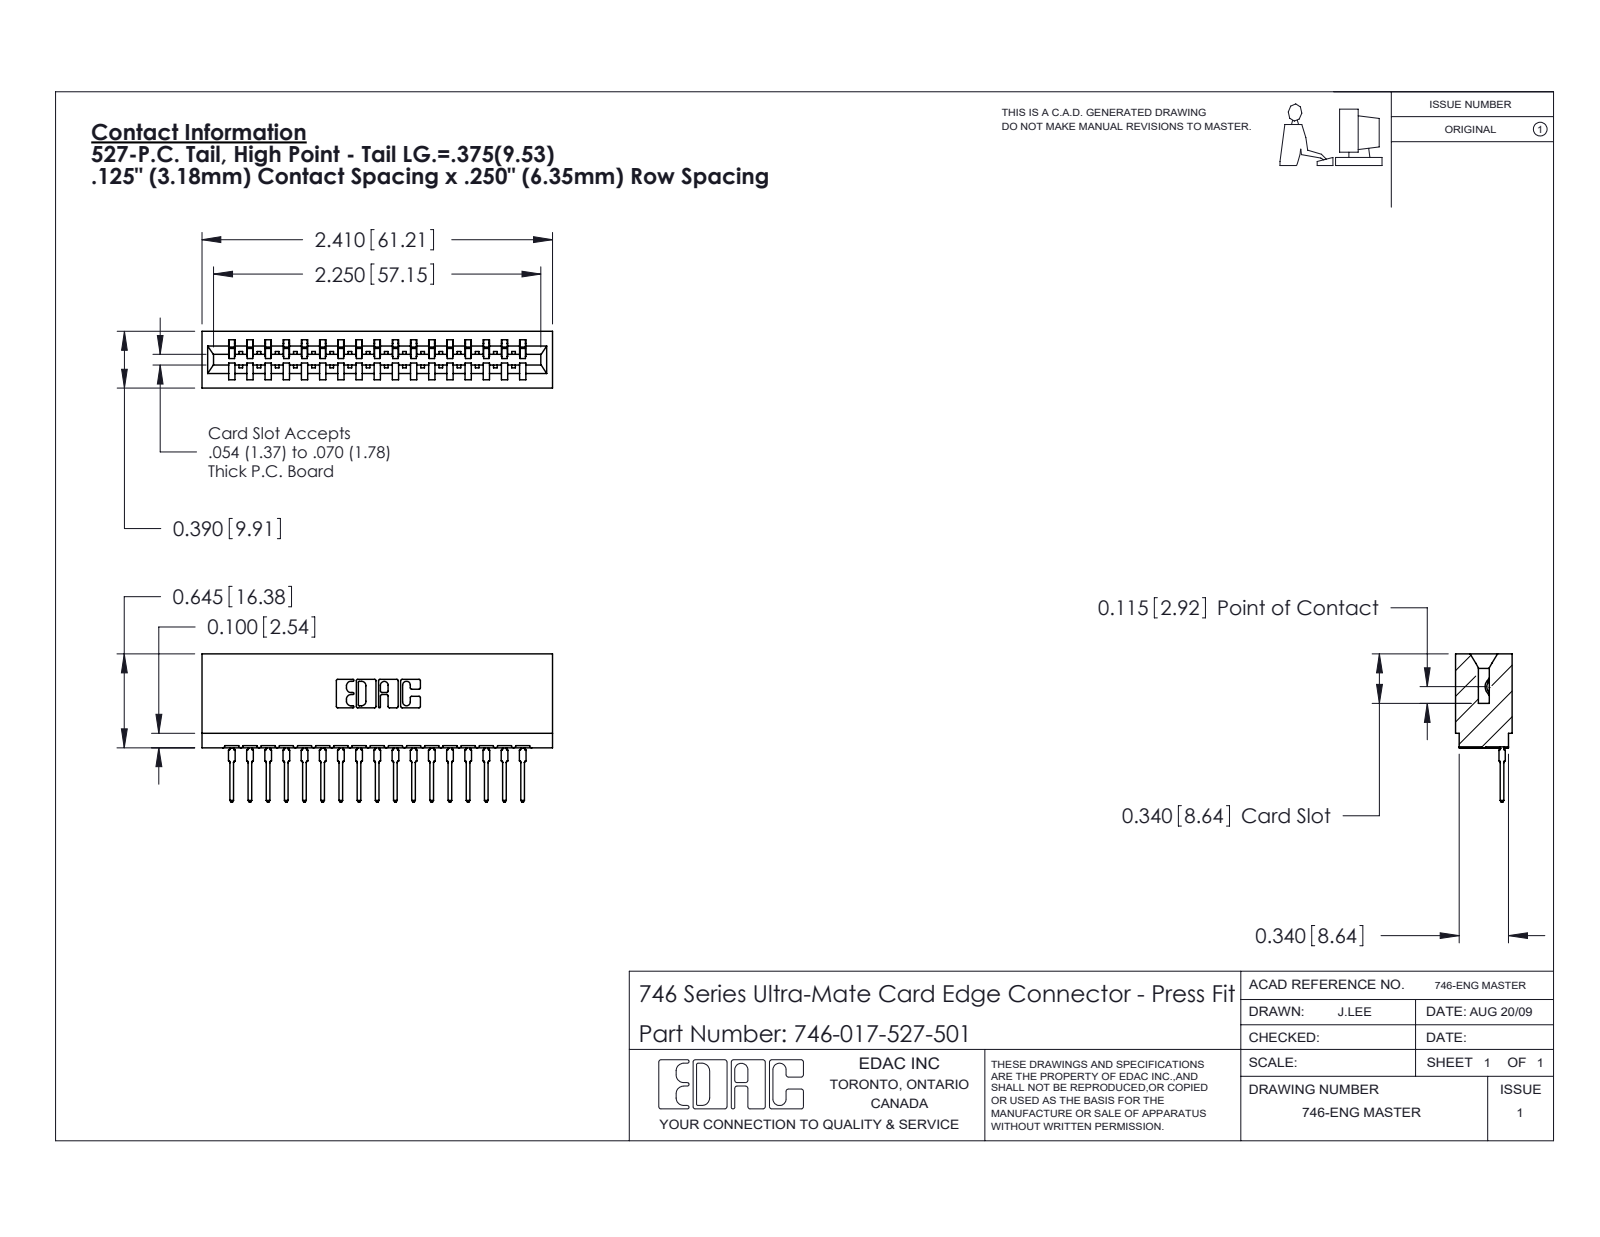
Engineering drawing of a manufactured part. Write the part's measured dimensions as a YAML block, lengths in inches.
part_name: "746-292-001_527; 746-017-527-501; 746 Part_.340 Slot Depth - 01"
step_written_by: "SolidWorks 2020 (CONFIG_CONTROL_DESIGN)"
units: inches
bodies: {solids: 18, faces: 1933, planar: 1126, cylindrical: 365, other: 442}
overall_size: [2.41, 1.019, 0.39]
volume: 0.43
surface_area: 14.28
partial_cylinders:
  - {radius: 0.021, count: 34}
  - {radius: 0.01, count: 22}
  - {radius: 0.015, count: 18}
  - {radius: 0.007, count: 6}
  - {radius: 0.031, count: 6}
  - {radius: 0.005, count: 4}
  - {radius: 0.011, count: 4}
  - {radius: 0.026, count: 3}
face_to_face_distances: [0.25, 0.057, 0.333, 0.39, 0.5, 0.042, 0.292, 0.375, 0.125, 0.025]
